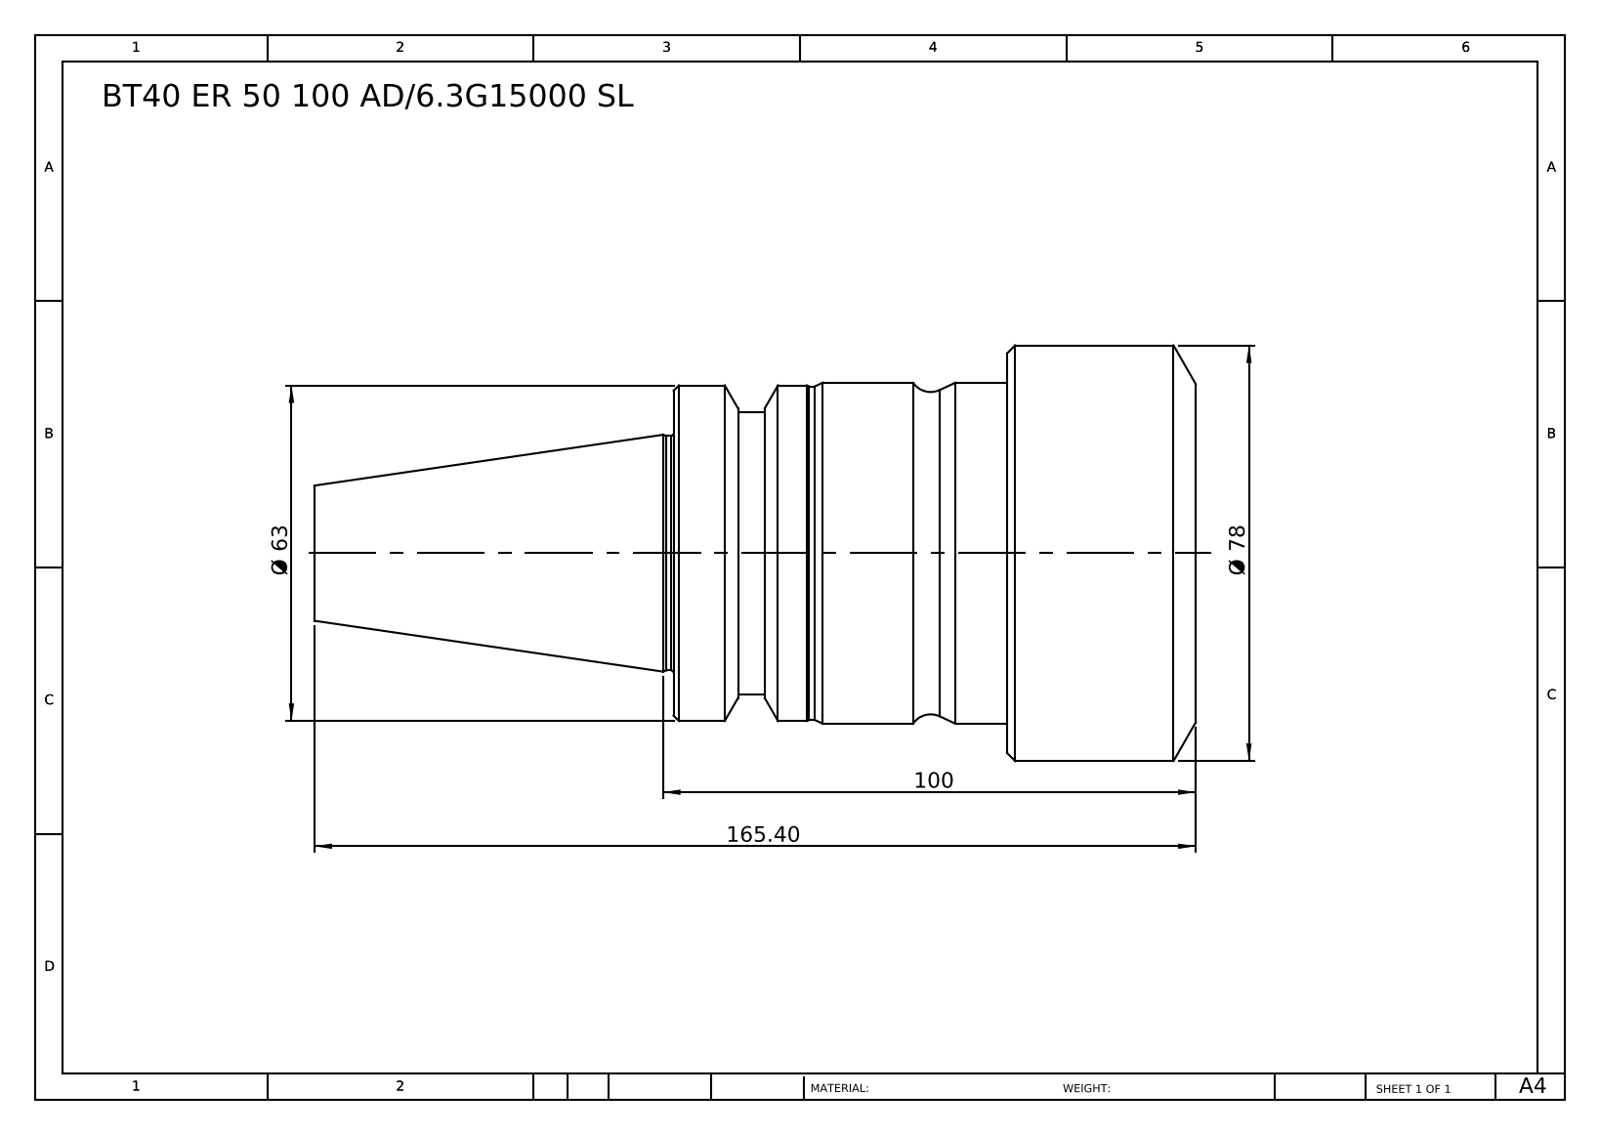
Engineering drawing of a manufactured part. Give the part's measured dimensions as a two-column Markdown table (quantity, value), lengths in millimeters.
| quantity | value |
| --- | --- |
| part name | BT40 ER 50 100 AD-6.3G15000 SL |
| STEP written by | SolidWorks 2014 (CONFIG_CONTROL_DESIGN) |
| units | millimeters |
| bodies | 1 solid, 52 faces (6 planar, 16 cylindrical, 30 other) |
| overall size | 165.4 × 78 × 78 |
| volume | 422 784 mm³ |
| surface area | 37 097 mm² |
| round bosses / shafts (diameter × count) | 78 × 1, 64 × 1, 63 × 1, 62.6 × 1, 53 × 1, 44 × 1 |
| main face-to-face distances | 98, 35.4, 62.6, 165.4, 130, 67.4, 85.9, 50.5, 12.1, 79.5 |
